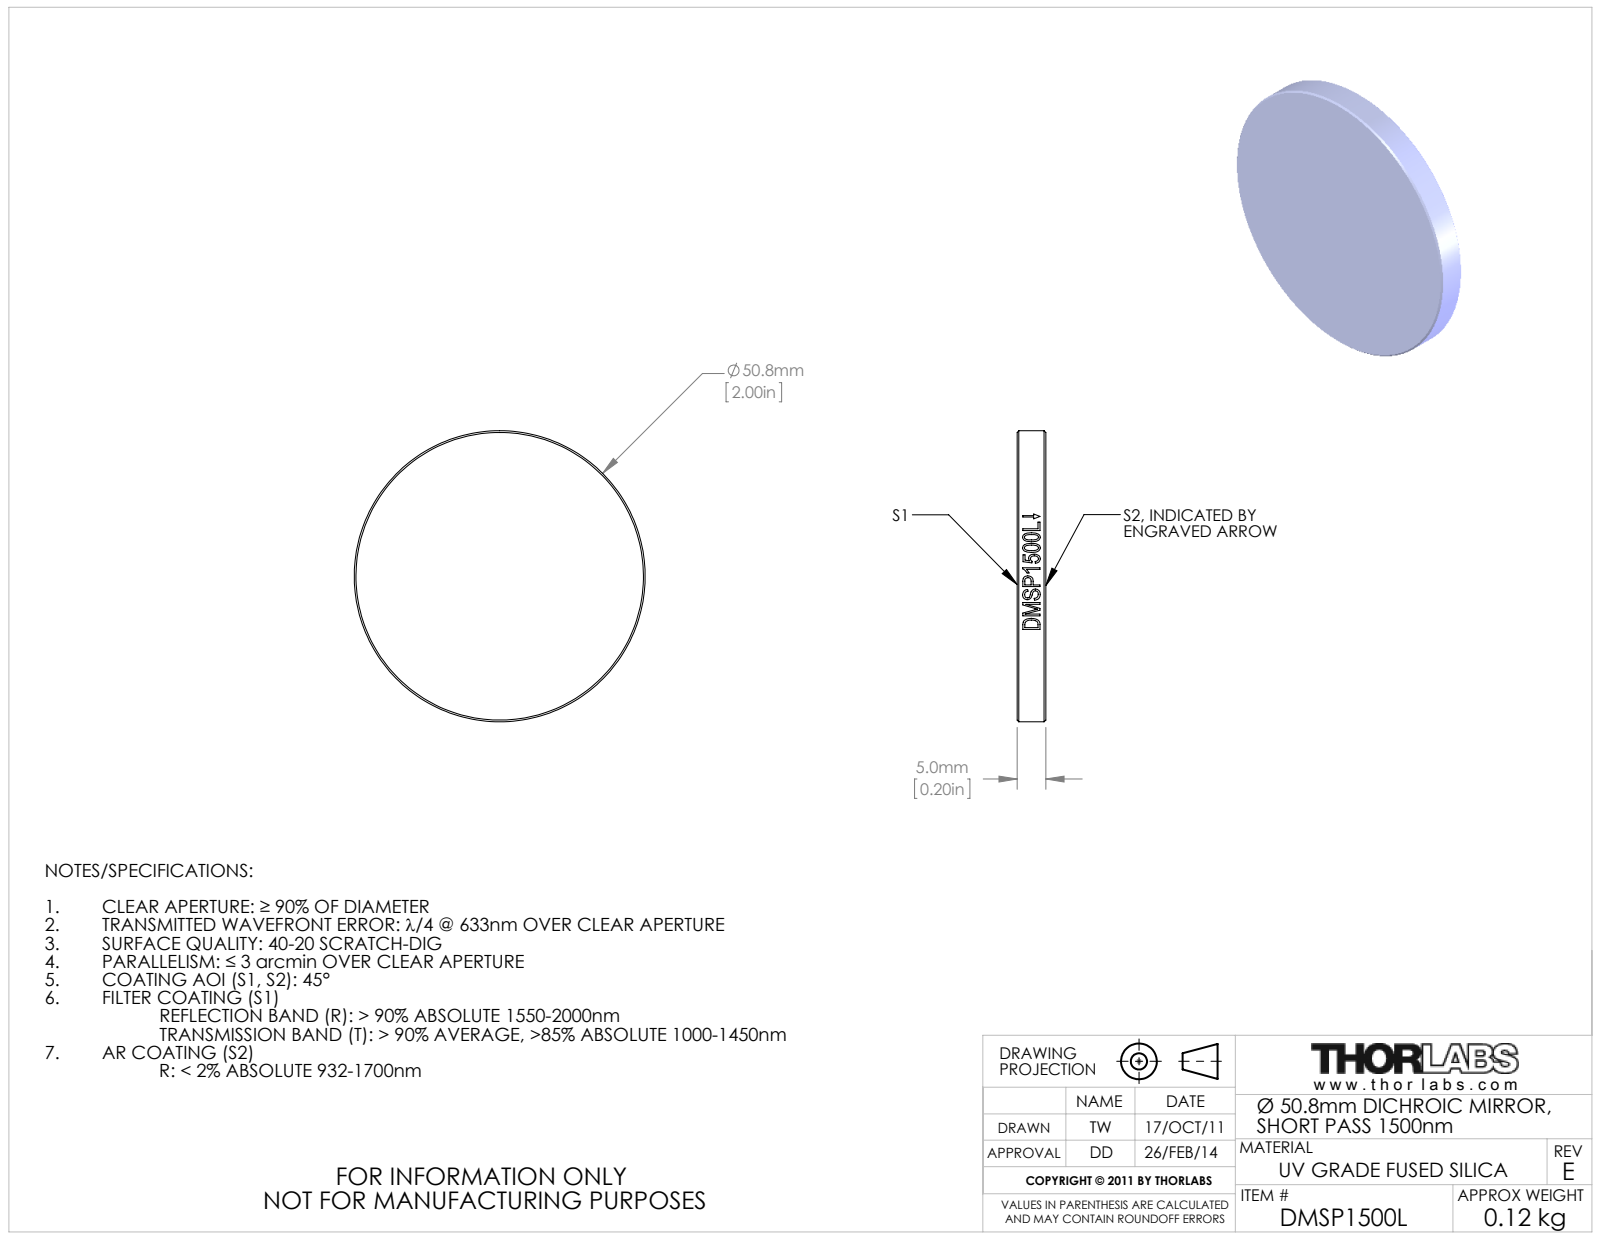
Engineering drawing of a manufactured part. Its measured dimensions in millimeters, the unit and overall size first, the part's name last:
Units: millimetres
Overall size (bounding box): 50.8 × 50.8 × 5
Round bosses / shafts (diameter × count): ⌀50.8 ×1
Main face-to-face distances: 5
Bodies: 0 solids, 22 faces (2 planar, 16 cylindrical, 4 other)
Part name (STEP PRODUCT): 21942-E0W
STEP written by: SolidWorks 2011 (CONFIG_CONTROL_DESIGN)
